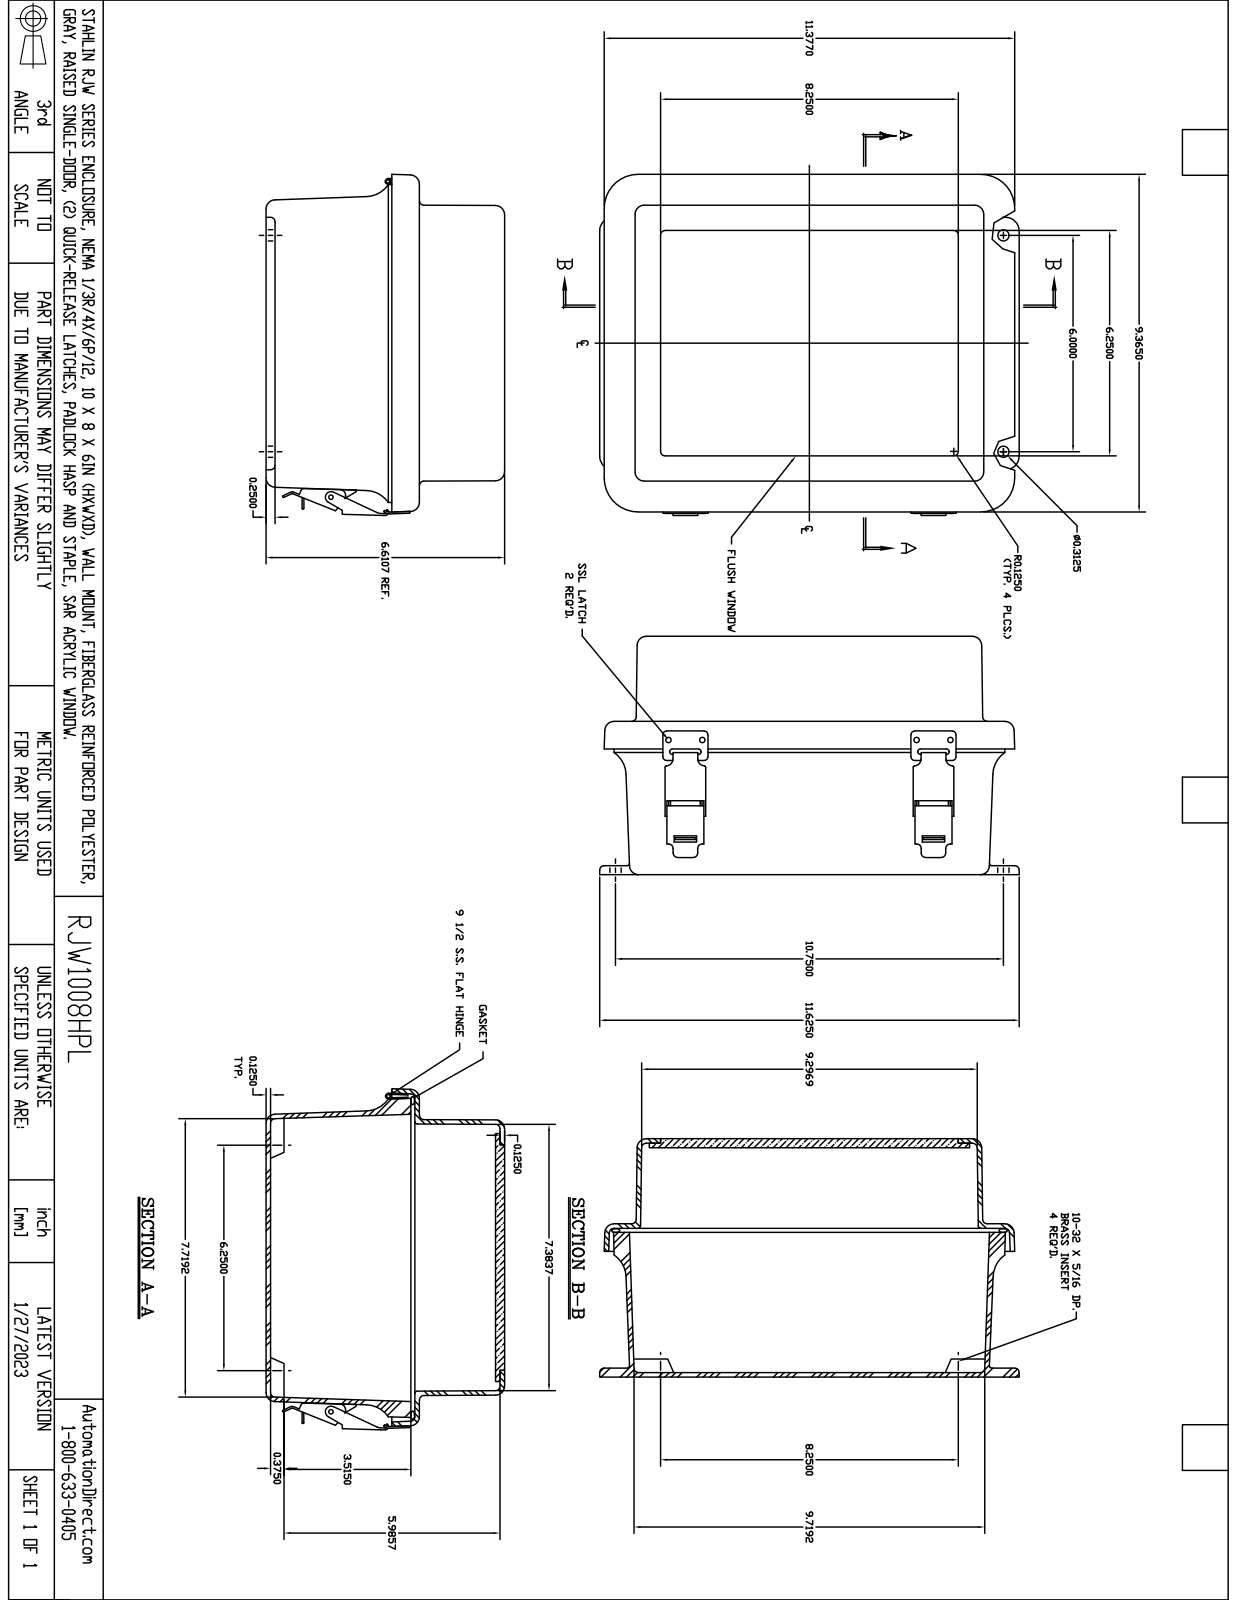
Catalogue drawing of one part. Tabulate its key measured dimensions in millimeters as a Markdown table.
| quantity | value |
| --- | --- |
| part name | MRW1008HPL |
| STEP written by | SolidWorks 2018 (AUTOMOTIVE_DESIGN) |
| units | millimeters |
| bodies | 39 solids, 1016 faces (424 planar, 421 cylindrical, 171 other) |
| overall size | 295.3 × 242.2 × 167.5 |
| volume | 1 257 000 mm³ |
| surface area | 656 100 mm² |
| round holes (diameter × count) | 3.6 × 20, 2.6 × 8, 3.3 × 8, 3.9 × 5, 3.3 × 4, 4 × 4, 5.5 × 4, 3.4 × 2, 9.5 × 2, 2.2 × 1, 2.2 × 1 |
| round bosses / shafts (diameter × count) | 3.2 × 13, 6.4 × 8, 6.9 × 4, 3.2 × 3, 7.6 × 1, 4.3 × 1, 3.9 × 1, 3.4 × 1 |
| partial cylindrical surfaces (radius × count) | 3.2 × 36, 0.4 × 20, 0.8 × 20, 1.1 × 16, 6.4 × 16, 0.8 × 12, 0.6 × 8, 1.5 × 6 |
| main face-to-face distances | 3.2, 161.1, 6.4, 167.5, 164.3, 158, 104.4, 56.8, 3.2, 101.2 |
| hole center spacings | 177.8, 178.8, 23.8, 152.4, 19.1, 76.2, 6.4, 19.1 |
